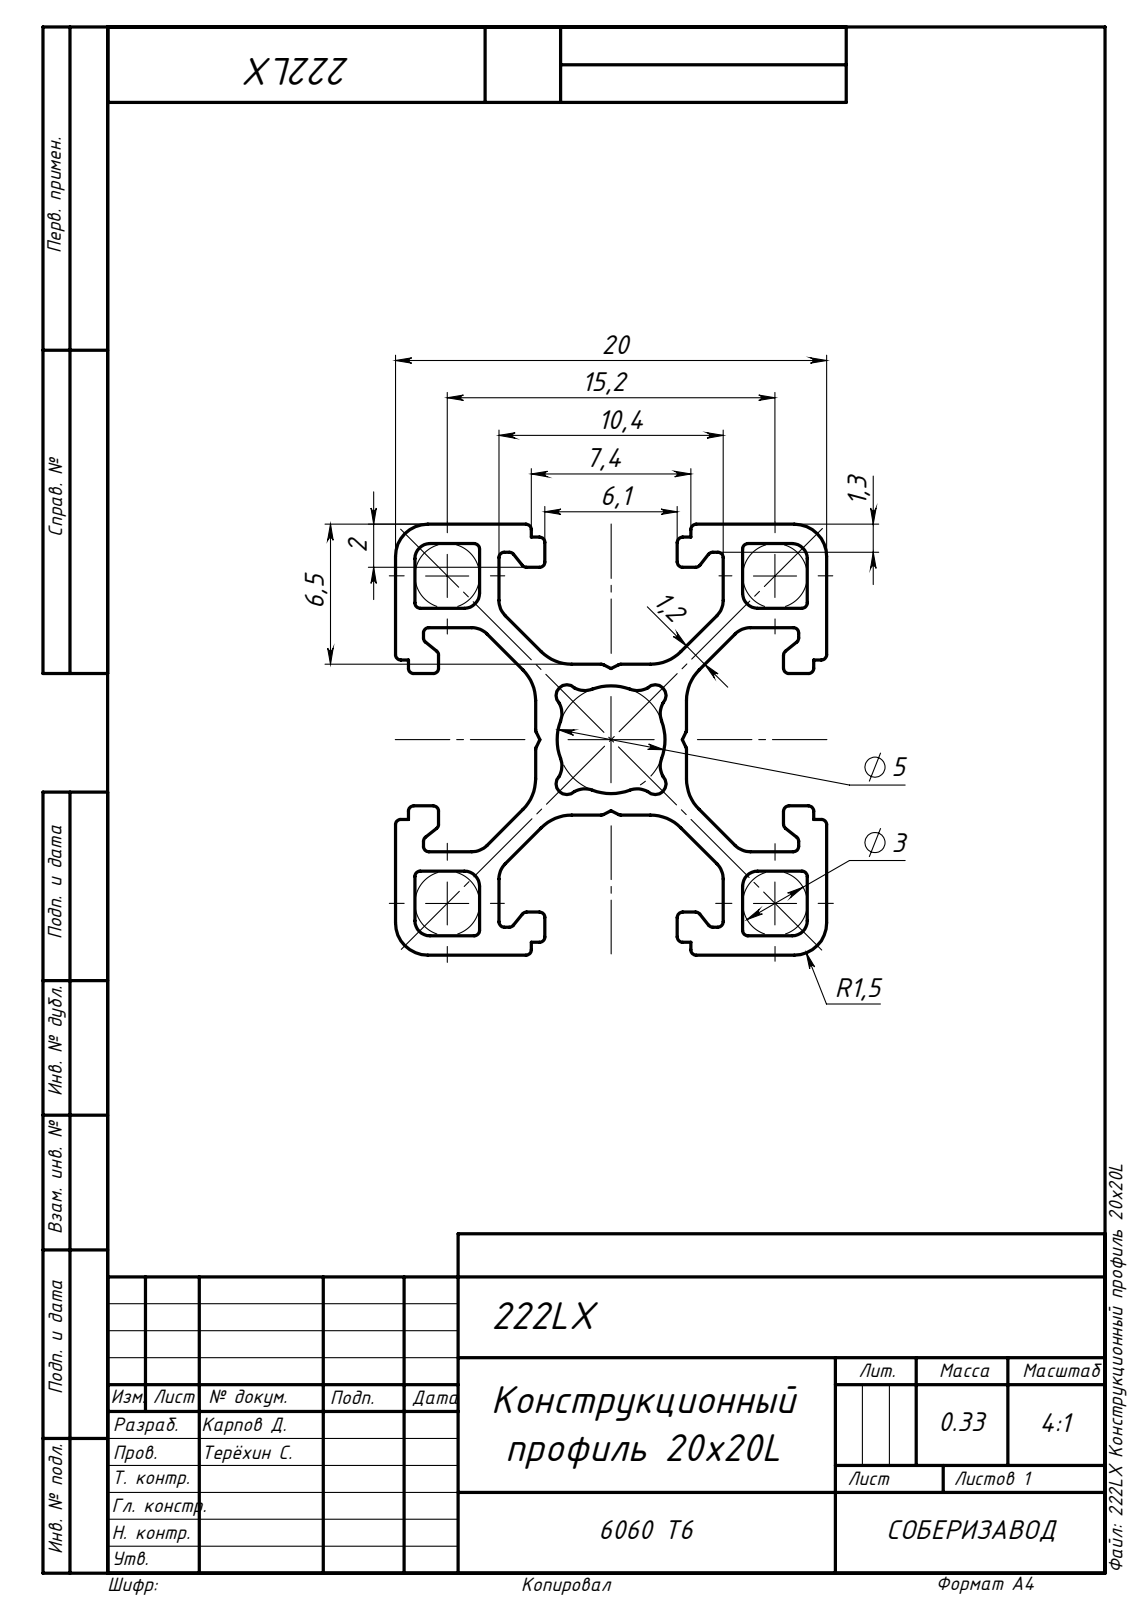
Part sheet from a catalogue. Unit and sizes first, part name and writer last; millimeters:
Units: millimetres
Overall size (bounding box): 1000 × 20 × 20
Partial cylindrical surfaces — rounded edges, fillets, slot ends (radius × count): R0.25 ×64, R1 ×16, R0.7 ×8, R2 ×8, R0.5 ×4, R1.5 ×4, R2.5 ×1
Main face-to-face distances: 0.9, 3.9, 15.2, 20, 19.1, 16.1, 3, 4.8, 14.3, 11.3
Volume: 121 651 mm³ · Surface area: 220 701 mm²
Bodies: 1 solid, 214 faces (106 planar, 108 cylindrical, 0 other)
STEP written by: SolidWorks 2019 (AUTOMOTIVE_DESIGN)
